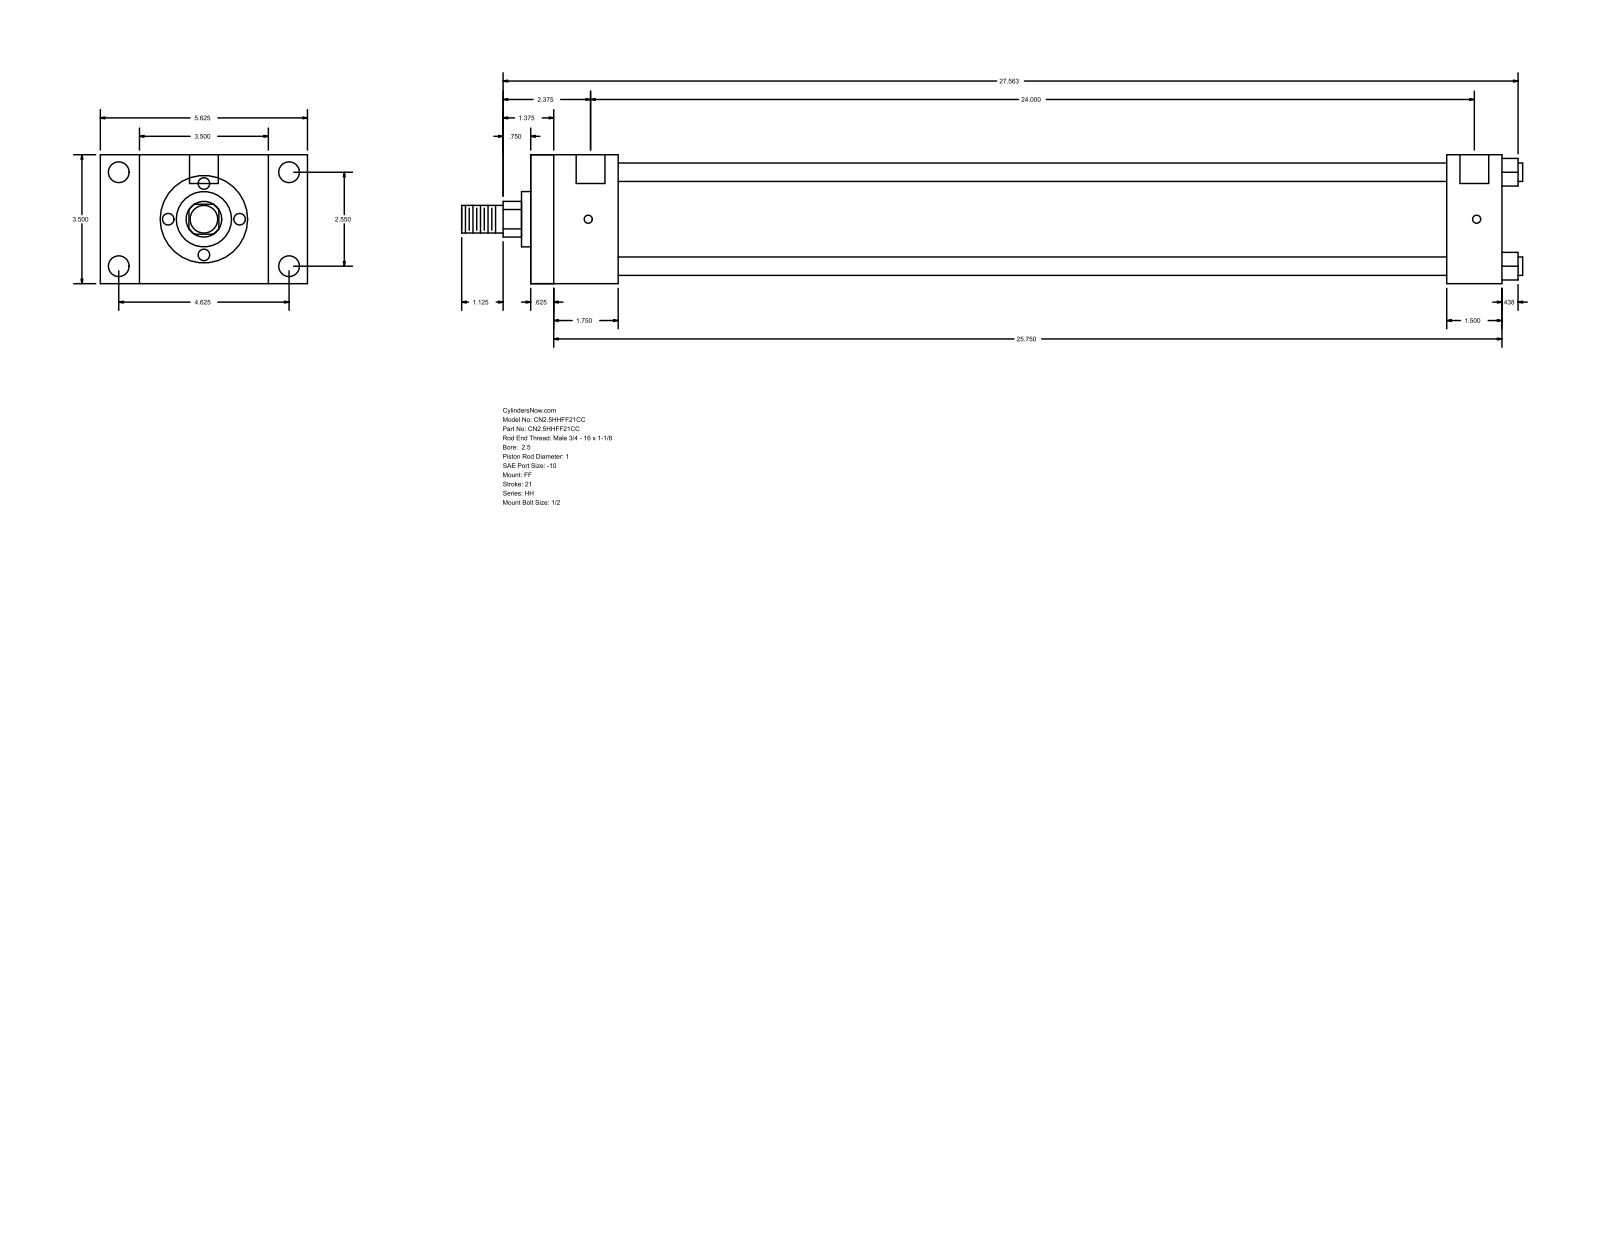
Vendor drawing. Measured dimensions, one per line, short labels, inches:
name: HH_FF__0250_1
written by: GSSL Pune (CONFIG_CONTROL_DESIGN)
unit: in
bodies: 0 solids, 92 faces (64 planar, 28 cylindrical, 0 other)
size: 28.813 × 5.625 × 3.5
holes: 4× ⌀0.219, 4× ⌀0.563, 2× ⌀0.781
bosses: 4× ⌀0.5, 1× ⌀2.875, 1× ⌀1.5, 1× ⌀1, 1× ⌀0.75
rounds: 1× R0.484
face distances: 3.5, 26.375, 0.625, 25.75, 1.5, 2.375, 1.75, 24, 24.875, 24.25
hole spacings: 0.063, 2.55, 4.625, 5.281, 24.062, 24.125, 24
